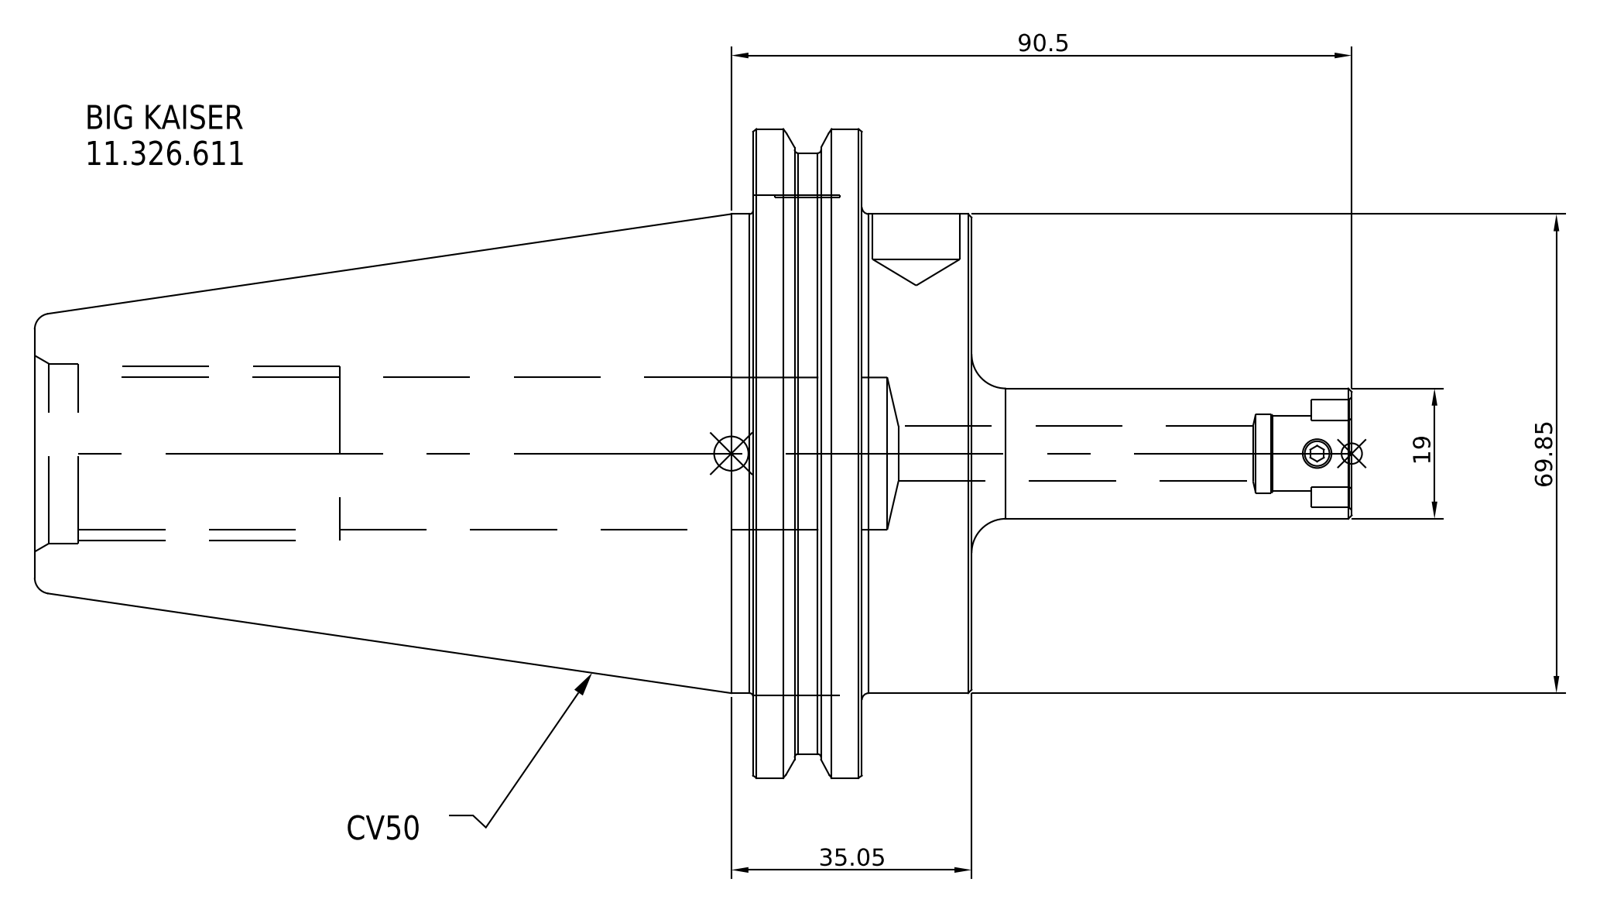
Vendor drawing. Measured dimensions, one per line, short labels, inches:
name: 11.326.611
written by: SolidWorks 2021 (CONFIG_CONTROL_DESIGN)
unit: in
bodies: 1 solid, 16 faces (7 planar, 6 cylindrical, 3 other)
size: 7.563 × 3.875 × 3.875
volume: 27.97 in³; area: 68.66 in²
bosses: 1× ⌀3.875, 1× ⌀3.594, 1× ⌀2.75, 1× ⌀0.75
face distances: 0.691, 0.628, 1.319, 5.378, 4.75, 4.059, 2.185, 2.813, 3.504, 7.563
